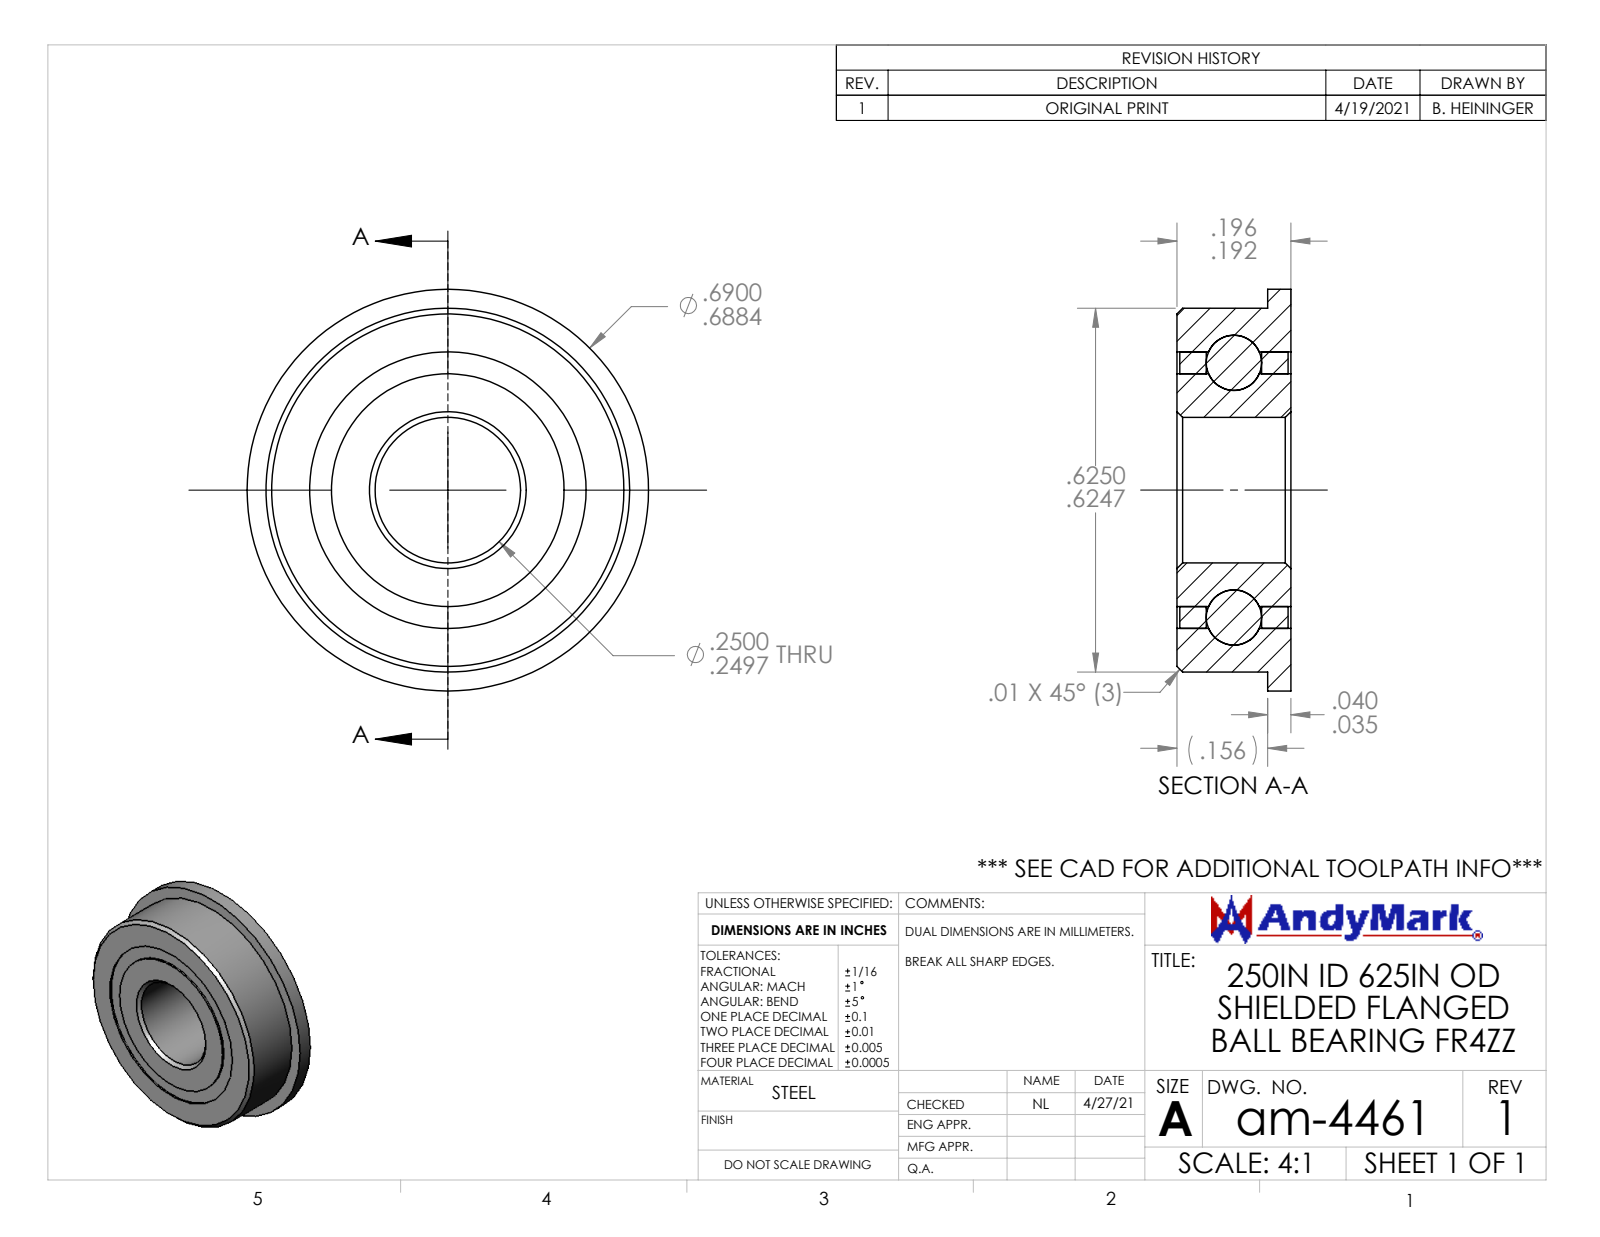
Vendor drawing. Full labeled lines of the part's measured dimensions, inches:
Part name (STEP PRODUCT): am-4461 1-4 in ID 5-8 in OD Shielded Flanged Bearing FR4ZZ
STEP written by: SolidWorks 2019 (AUTOMOTIVE_DESIGN)
Units: inches
Bodies: 18 solids, 71 faces (9 planar, 22 cylindrical, 40 other)
Overall size (bounding box): 0.69 × 0.69 × 0.196
Volume: 0.049 in³ · Surface area: 2.53 in²
Round holes (diameter × count): ⌀0.25 ×1, ⌀0.4 ×1, ⌀0.475 ×1
Round bosses / shafts (diameter × count): ⌀0.69 ×1, ⌀0.625 ×1
Main face-to-face distances: 0.196, 0.191, 0.05, 0.146, 0.045, 0.141, 0.04, 0.156, 0.035, 0.186
